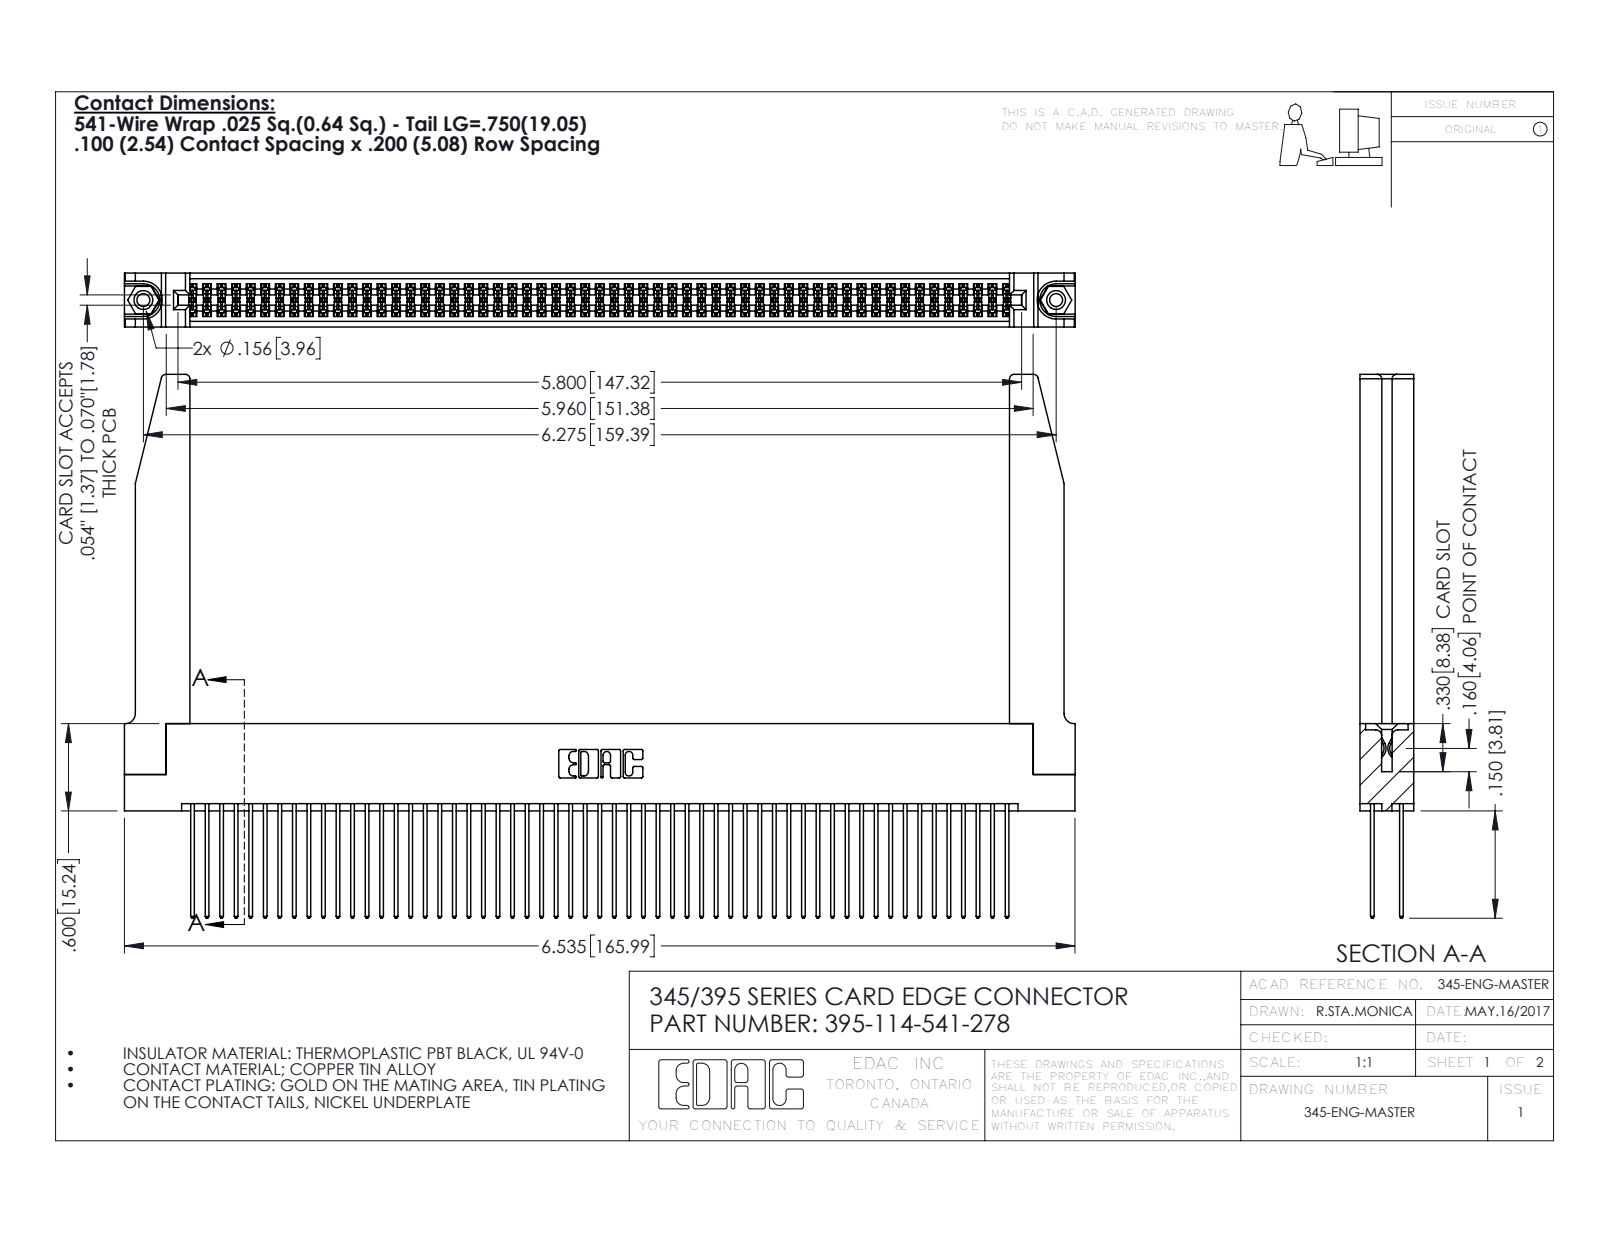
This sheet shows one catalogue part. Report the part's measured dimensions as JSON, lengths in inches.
{"part_name": "345-292-001_345-293-141; 395-114-541-278; 345-250-001_345-250-001-102; 345 Part_Flush Mounting Lugs - 0.156 Dia-TH (+1 more)", "step_written_by": "SolidWorks 2016 (CONFIG_CONTROL_DESIGN)", "units": "inches", "bodies": {"solids": 119, "faces": 6060, "planar": 3984, "cylindrical": 2024, "other": 52}, "overall_size": [6.536, 3.737, 0.37], "volume_in3": 1.507, "surface_area_in2": 54.58, "round_holes": [[0.089, 2], [0.125, 2], [0.156, 2], [0.064, 1]], "round_bosses_or_shafts": [[0.155, 2]], "partial_cylinders_radius": [[0.006, 171], [0.01, 114], [0.01, 22], [0.03, 8], [0.007, 6], [0.031, 6], [0.026, 3], [0.014, 2]], "face_to_face_distances": [0.072, 0.298, 0.2, 0.37, 0.098, 0.272, 0.025, 0.225, 0.175, 0.148], "hole_center_spacings": [0.27, 6.039, 6.275]}
